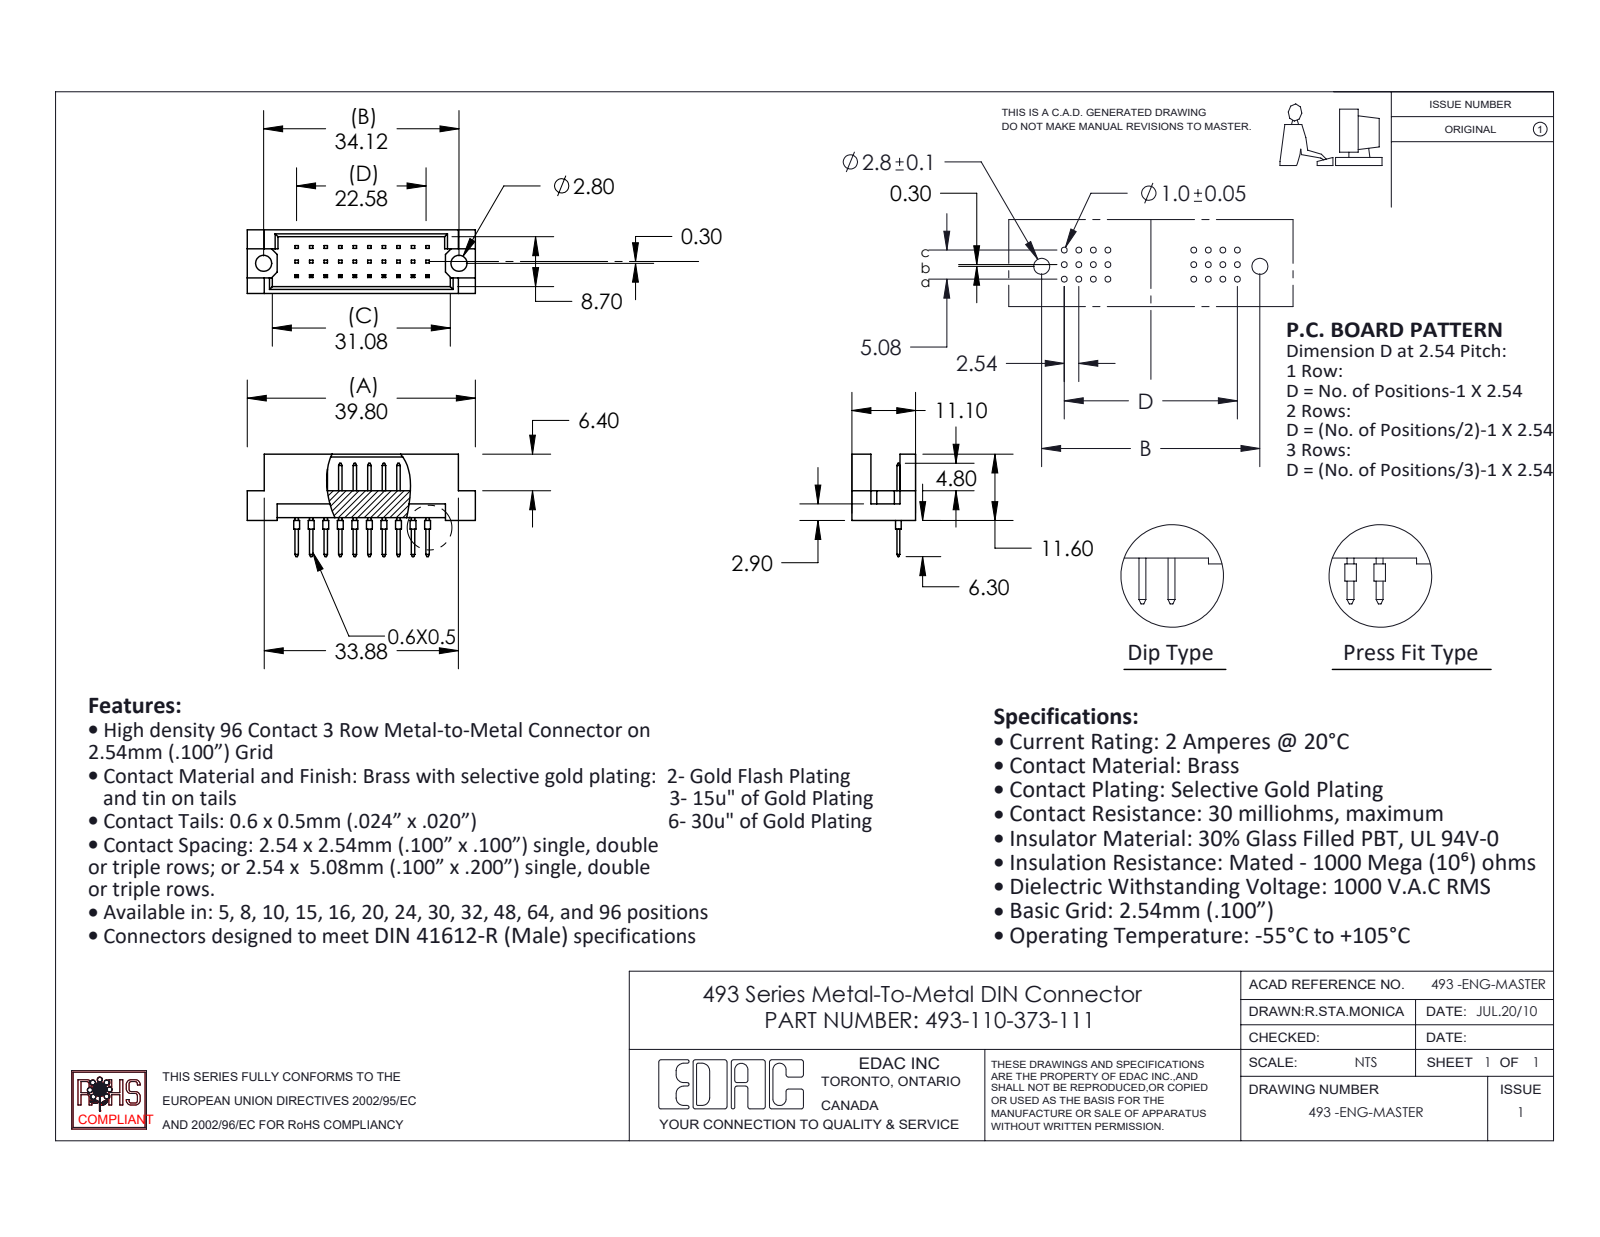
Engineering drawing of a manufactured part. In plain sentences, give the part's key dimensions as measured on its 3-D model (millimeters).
The part is named "493-290_73; 493-110-373-112; 493 Part_30". Its 3-D file was written by "SolidWorks 2020 (CONFIG_CONTROL_DESIGN)". It is 11 solids with 392 faces: 368 planar, 24 cylindrical and 0 other. Overall it measures 39.8 by 17.9 by 11.1 millimeters. Its volume is 2 428 cubic millimeters and its surface area 3 116 square millimeters. Round holes: 2 of diameter 2.8. Round bosses or shafts: 10 of diameter 1. The main face-to-face distances are 1.2, 9.9, 11.1, 8.7, 2.54, 0.5, 4.7, 5.08, 2.76, 3.26. The hole center spacings are 34.12.
